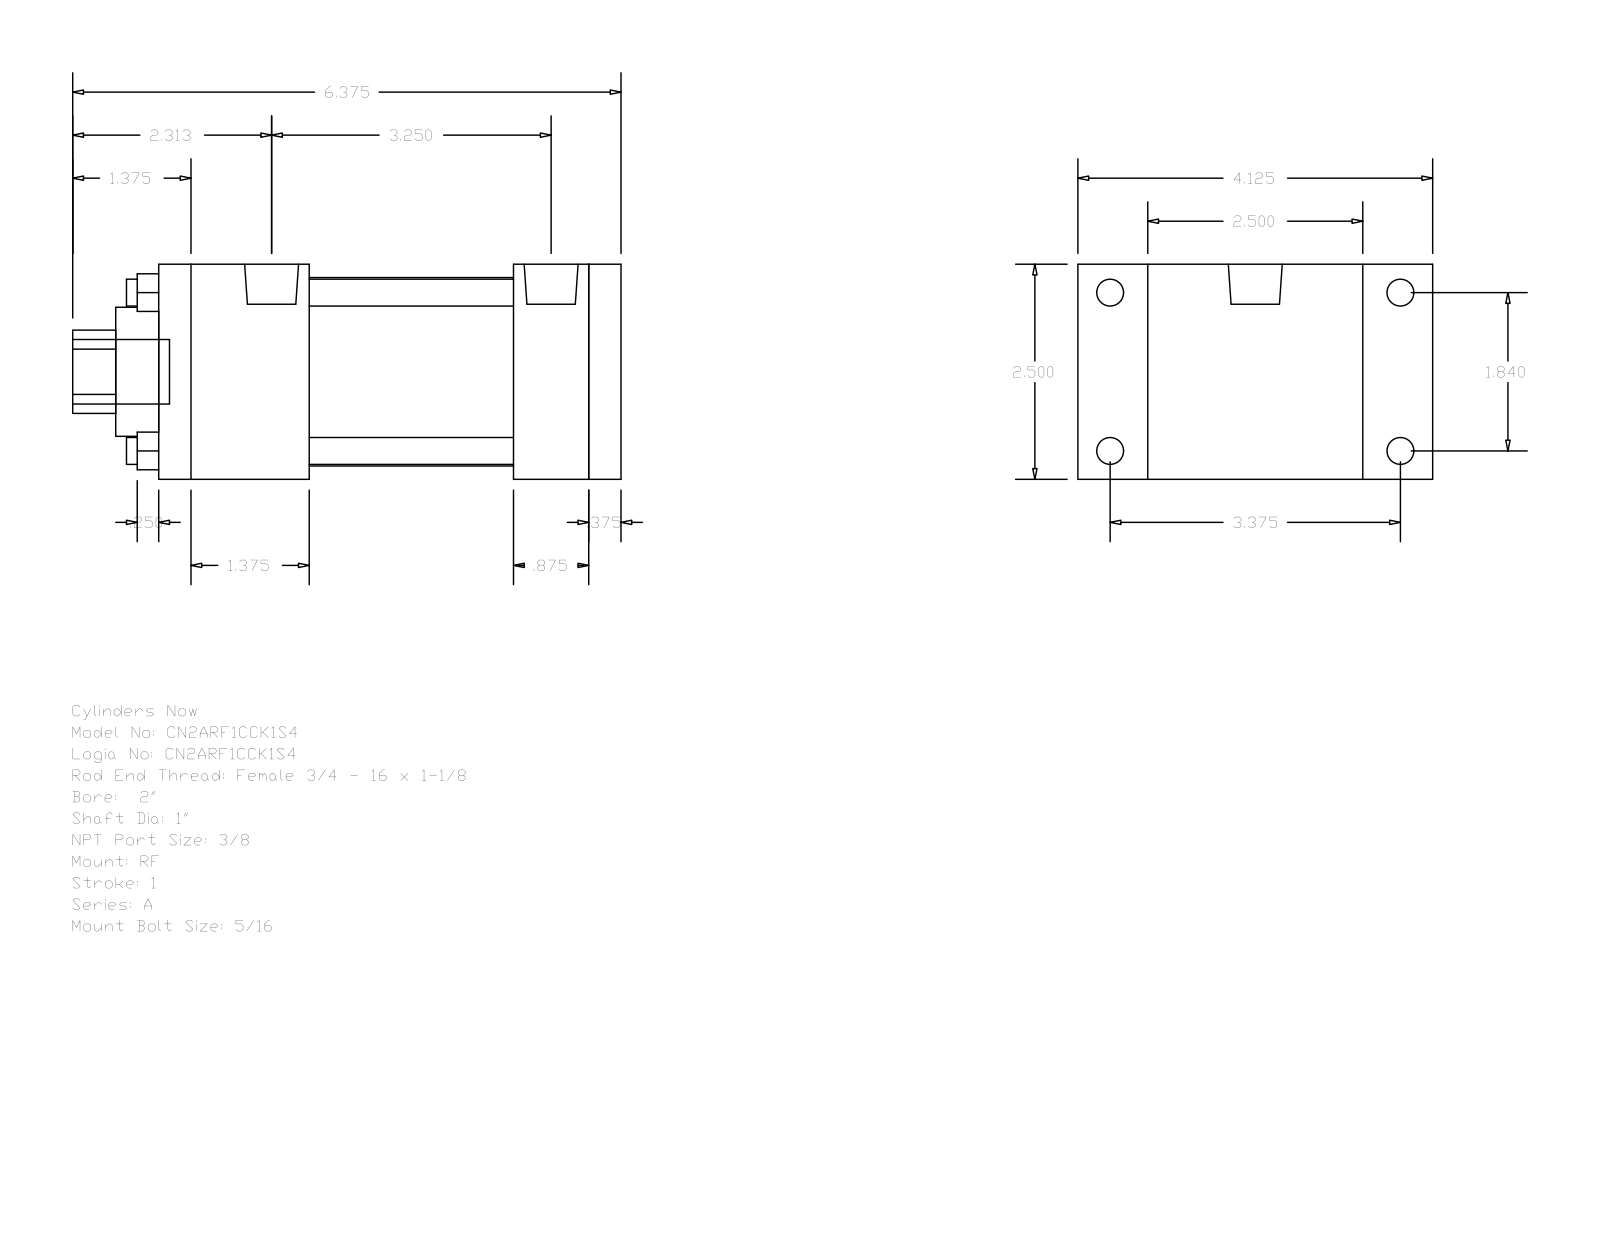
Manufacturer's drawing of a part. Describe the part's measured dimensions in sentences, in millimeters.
The part is named "A_RF__0200_1". Its 3-D file was written by "GSSL Pune (CONFIG_CONTROL_DESIGN)". It is 0 solids with 92 faces: 64 planar, 28 cylindrical and 0 other. Overall it measures 161.93 by 104.78 by 63.5 millimeters. Round holes: 4 of diameter 7.94, 1 of diameter 25.4, 1 of diameter 38.1, 1 of diameter 55.63. Round bosses or shafts: 4 of diameter 7.94, 4 of diameter 5.56, 2 of diameter 15.93, 1 of diameter 19.05. Partial cylindrical surfaces (rounded edges, fillets, slot ends): 1 of radius 12.29. The main face-to-face distances are 63.5, 9.53, 136.53, 127, 104.78, 20.64, 44.45, 82.55, 92.08, 60.33. The hole center spacings are 33.05, 46.74, 66.1.
